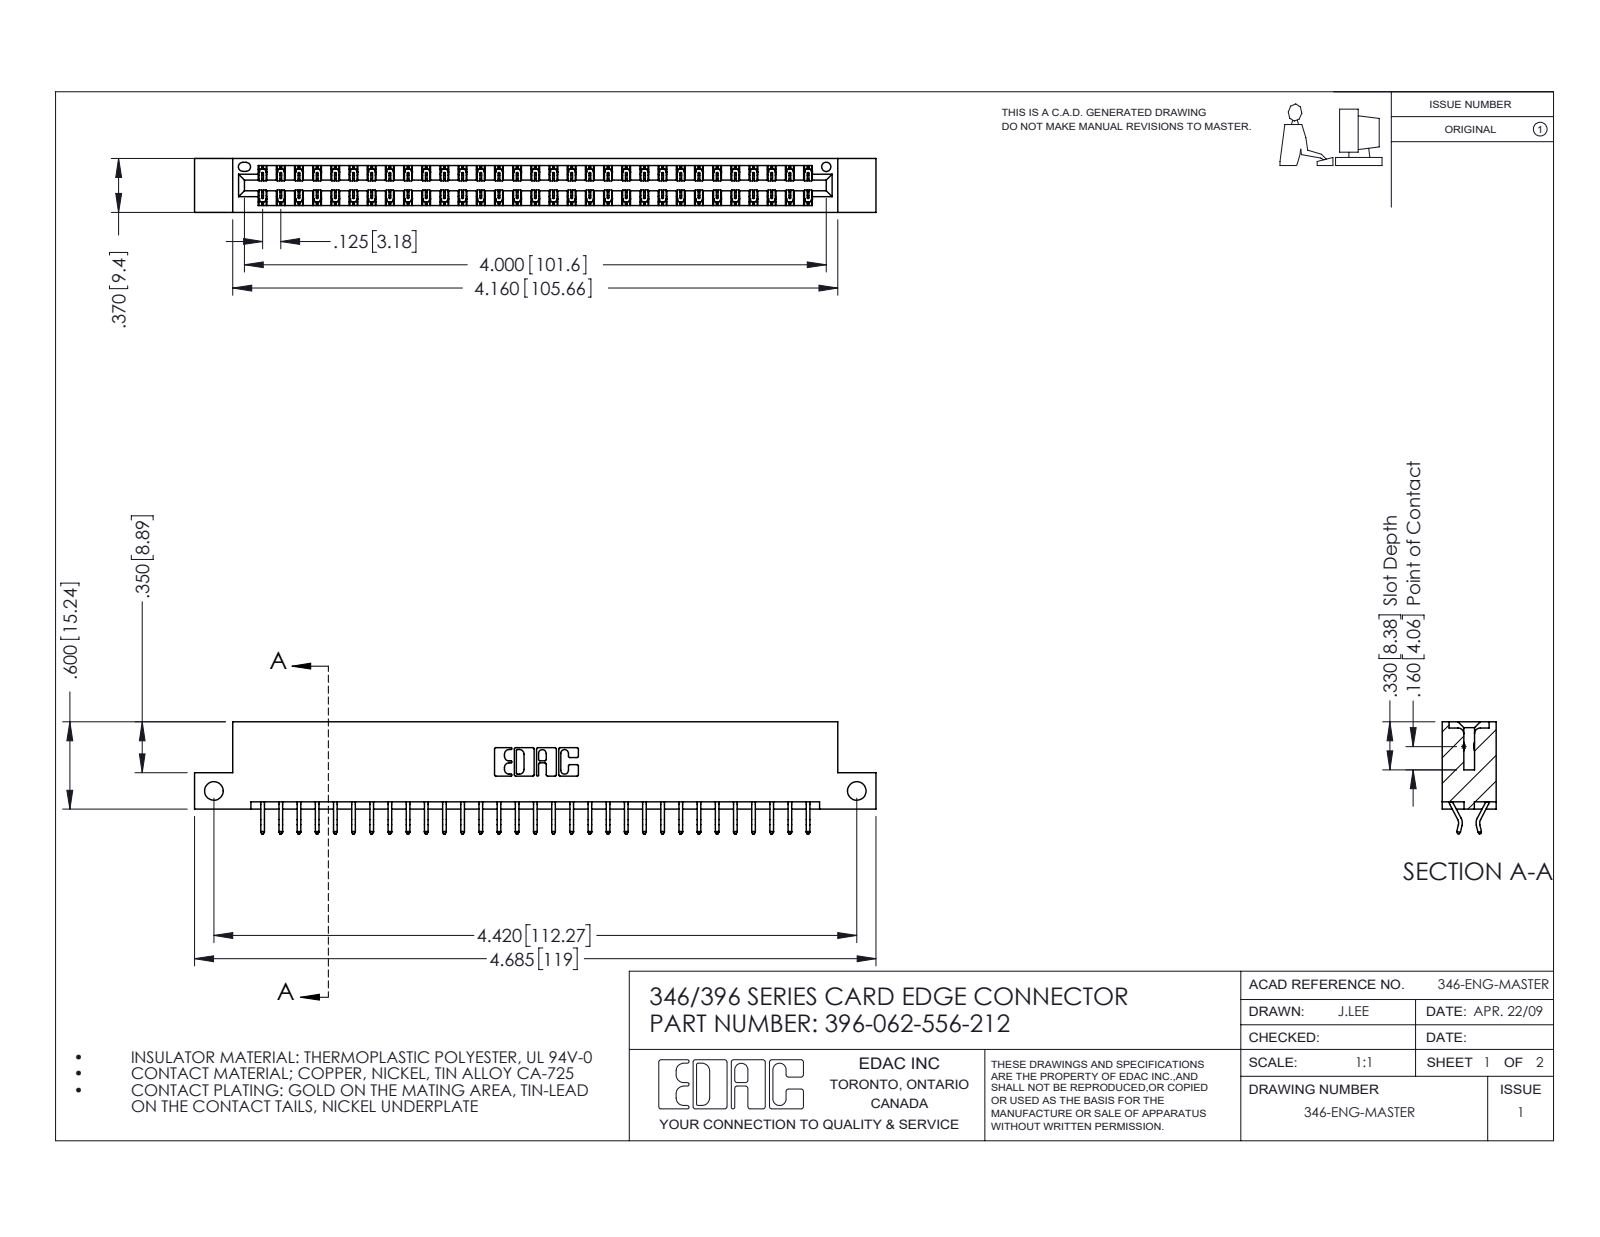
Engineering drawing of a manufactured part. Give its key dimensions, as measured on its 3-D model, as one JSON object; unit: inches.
{"part_name": "345-292-001_556 Tail; 396-062-556-212; 346 Part_Flush Mounting Lugs - Side Mount", "step_written_by": "SolidWorks 2016 (CONFIG_CONTROL_DESIGN)", "units": "inches", "bodies": {"solids": 63, "faces": 3718, "planar": 2494, "cylindrical": 1224, "other": 0}, "overall_size": [4.685, 0.77, 0.37], "volume_in3": 0.697, "surface_area_in2": 23.78, "round_holes": [[0.128, 2], [0.064, 1]], "partial_cylinders_radius": [[0.006, 93], [0.01, 22], [0.007, 6], [0.031, 6], [0.026, 3], [0.01, 2], [0.014, 2], [0.022, 2]], "face_to_face_distances": [0.048, 0.322, 0.37, 0.25, 0.025, 0.072, 0.298, 0.275, 0.148, 0.222], "hole_center_spacings": [4.42]}
